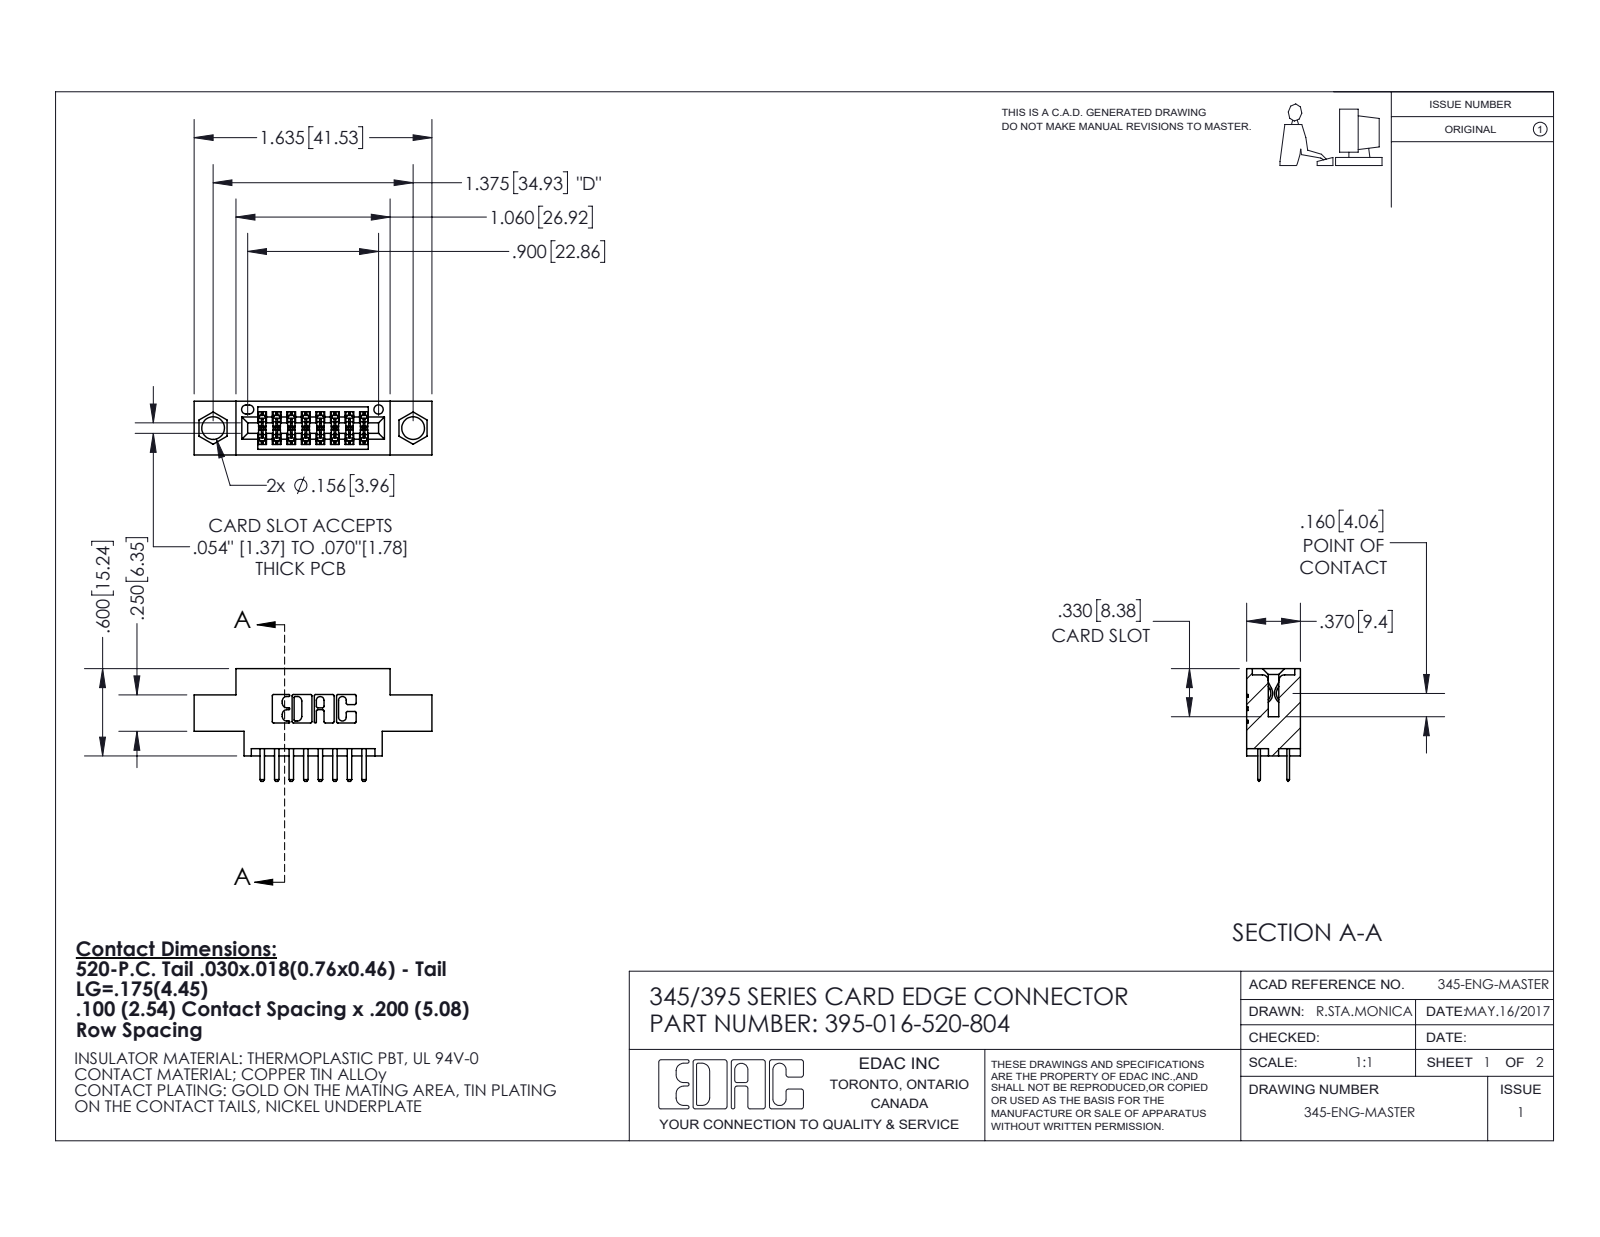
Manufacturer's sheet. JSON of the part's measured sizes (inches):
{"part_name": "345 Part_0.170 Offset - 0.156 Dia-TI; 395-016-520-804; 345-292-001_345-293-120", "step_written_by": "SolidWorks 2020 (CONFIG_CONTROL_DESIGN)", "units": "inches", "bodies": {"solids": 17, "faces": 1008, "planar": 658, "cylindrical": 350, "other": 0}, "overall_size": [1.635, 0.775, 0.37], "volume_in3": 0.213, "surface_area_in2": 6.95, "round_holes": [[0.156, 2], [0.064, 1]], "partial_cylinders_radius": [[0.006, 24], [0.01, 22], [0.01, 20], [0.007, 6], [0.031, 6], [0.026, 3], [0.014, 2], [0.019, 2]], "face_to_face_distances": [0.2, 0.37, 0.072, 0.298, 0.1, 0.098, 0.272, 0.025, 0.225, 0.06], "hole_center_spacings": [0.27, 1.144, 1.375]}
